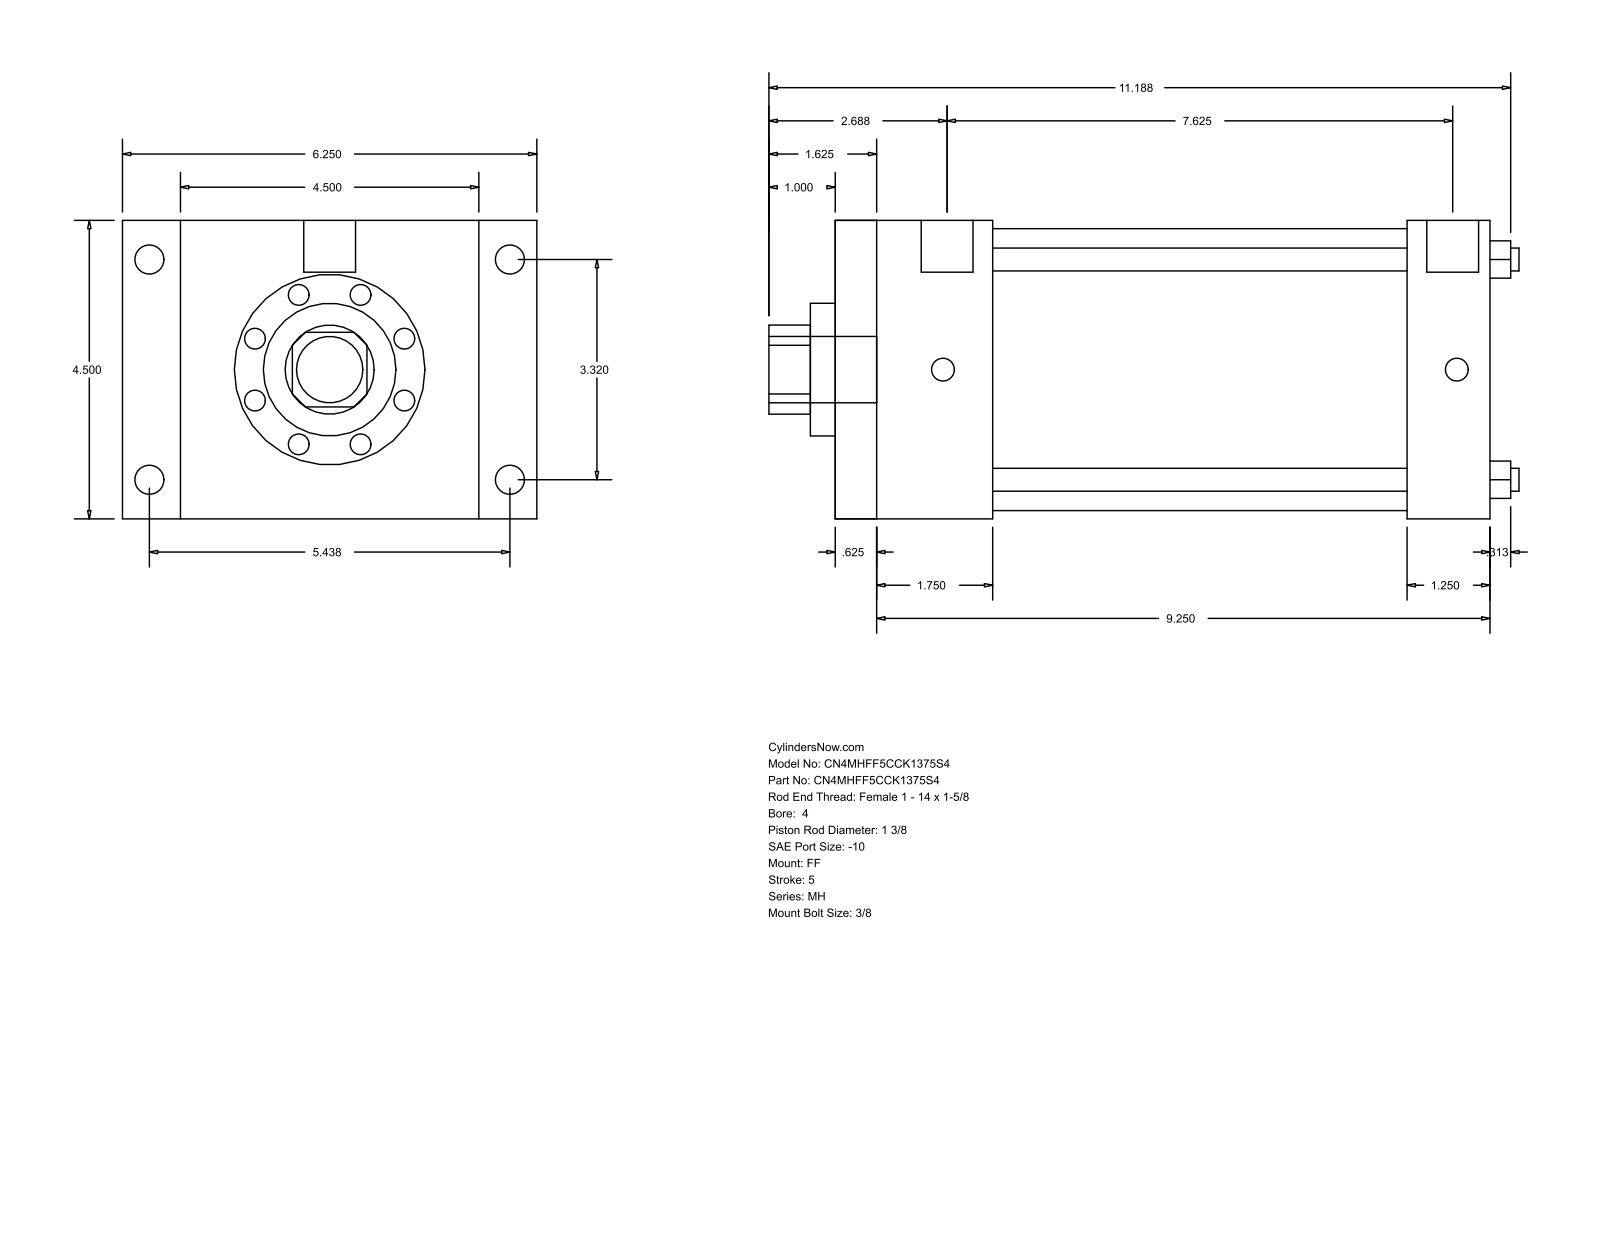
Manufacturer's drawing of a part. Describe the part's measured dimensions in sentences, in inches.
The part is named "MH_FF__0400_1.375". Its 3-D file was written by "GSSL Pune (CONFIG_CONTROL_DESIGN)". It is 0 solids with 92 faces: 64 planar, 28 cylindrical and 0 other. Overall it measures 11.313 by 6.25 by 4.5 inches. Round holes: 4 of diameter 0.345, 1 of diameter 1.375, 1 of diameter 2, 1 of diameter 4.25. Round bosses or shafts: 4 of diameter 0.438, 4 of diameter 0.344, 2 of diameter 0.781, 1 of diameter 1. Partial cylindrical surfaces (rounded edges, fillets, slot ends): 1 of radius 0.672. The main face-to-face distances are 4.5, 9.875, 0.625, 9.25, 2.375, 1.75, 7.5, 8.625, 8, 6.25. The hole center spacings are 2.347, 3.32, 4.695.
